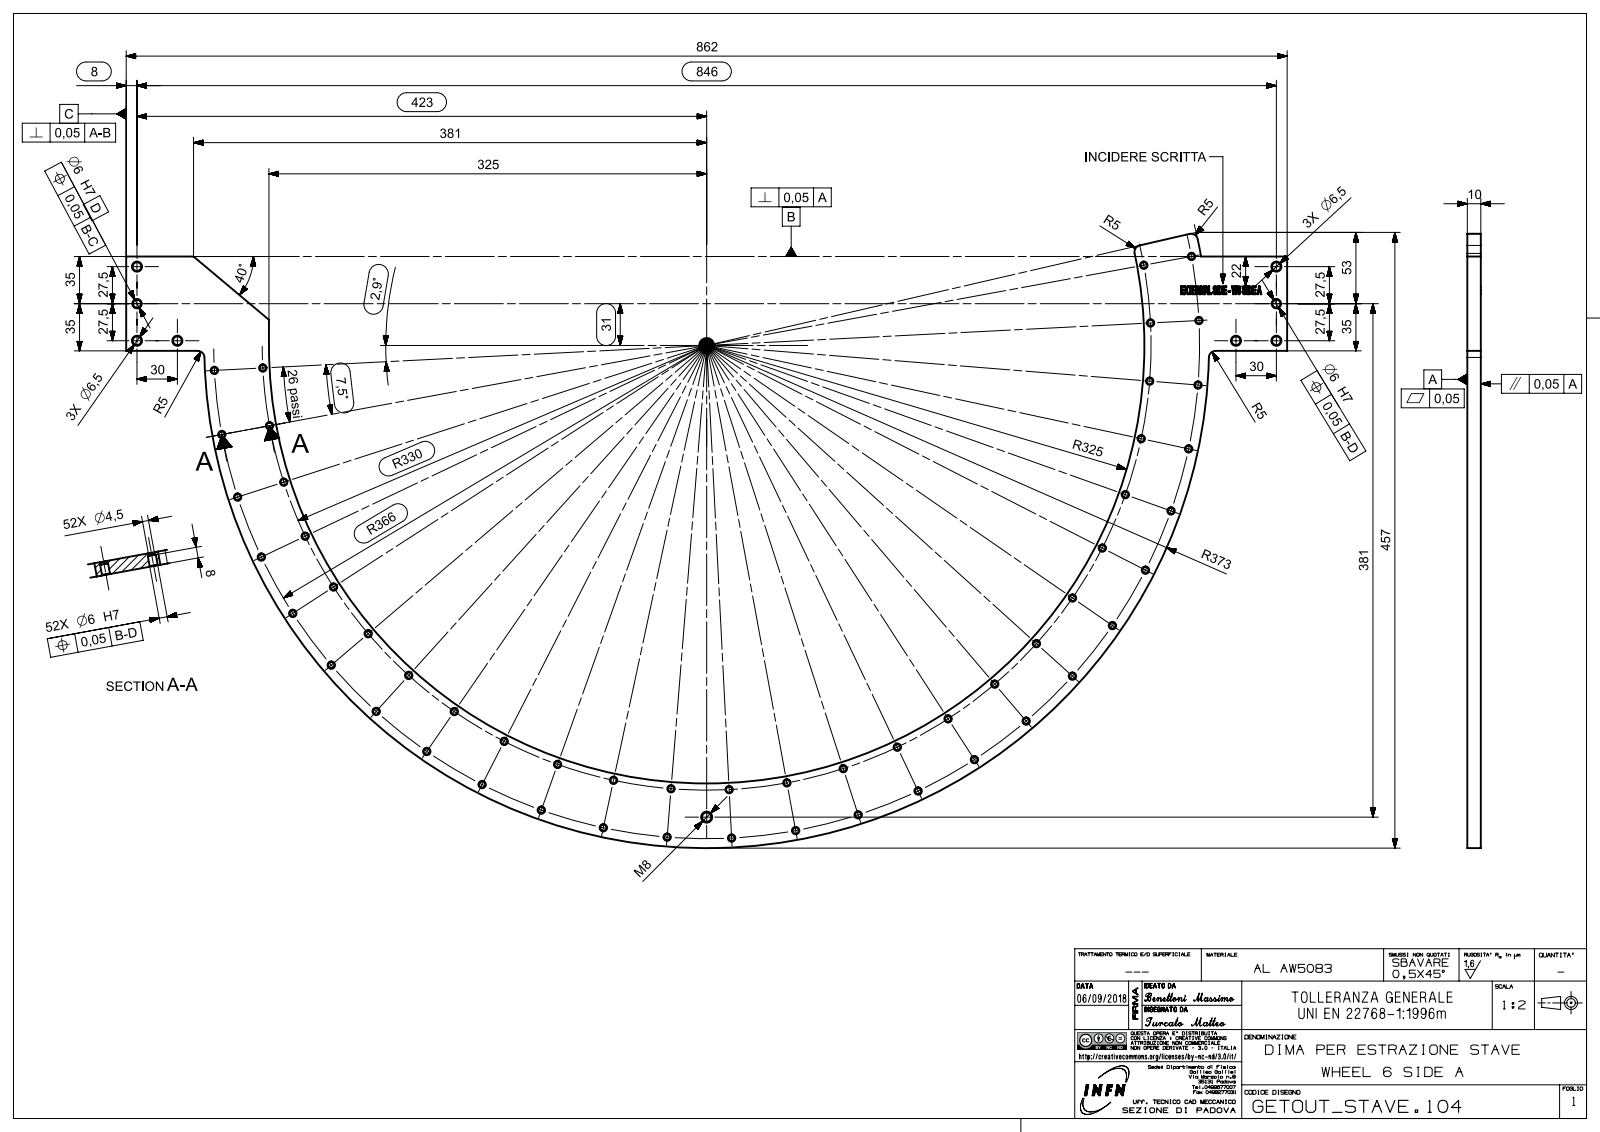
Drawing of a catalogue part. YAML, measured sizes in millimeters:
part_name: "bezA730AE56cd18"
step_written_by: "SIEMENS PLM Software NX 12.0 (AUTOMOTIVE_DESIGN)"
units: millimeters
bodies: {solids: 1, faces: 503, planar: 224, cylindrical: 120, other: 159}
overall_size: [862, 455.9, 10]
volume: 648634
surface_area: 169392
round_holes:
  - {diameter: 6, count: 54}
  - {diameter: 4.5, count: 52}
  - {diameter: 6.5, count: 6}
  - {diameter: 6.8, count: 1}
partial_cylinders:
  - {radius: 5, count: 4}
  - {radius: 325, count: 1}
  - {radius: 373, count: 1}
face_to_face_distances: [10, 70, 862, 8, 2, 756, 106, 9.5, 1.5, 0.5]
hole_center_spacings: [140.3, 57.99, 183.46, 97.61, 309.52, 36, 57.98, 97.6]
